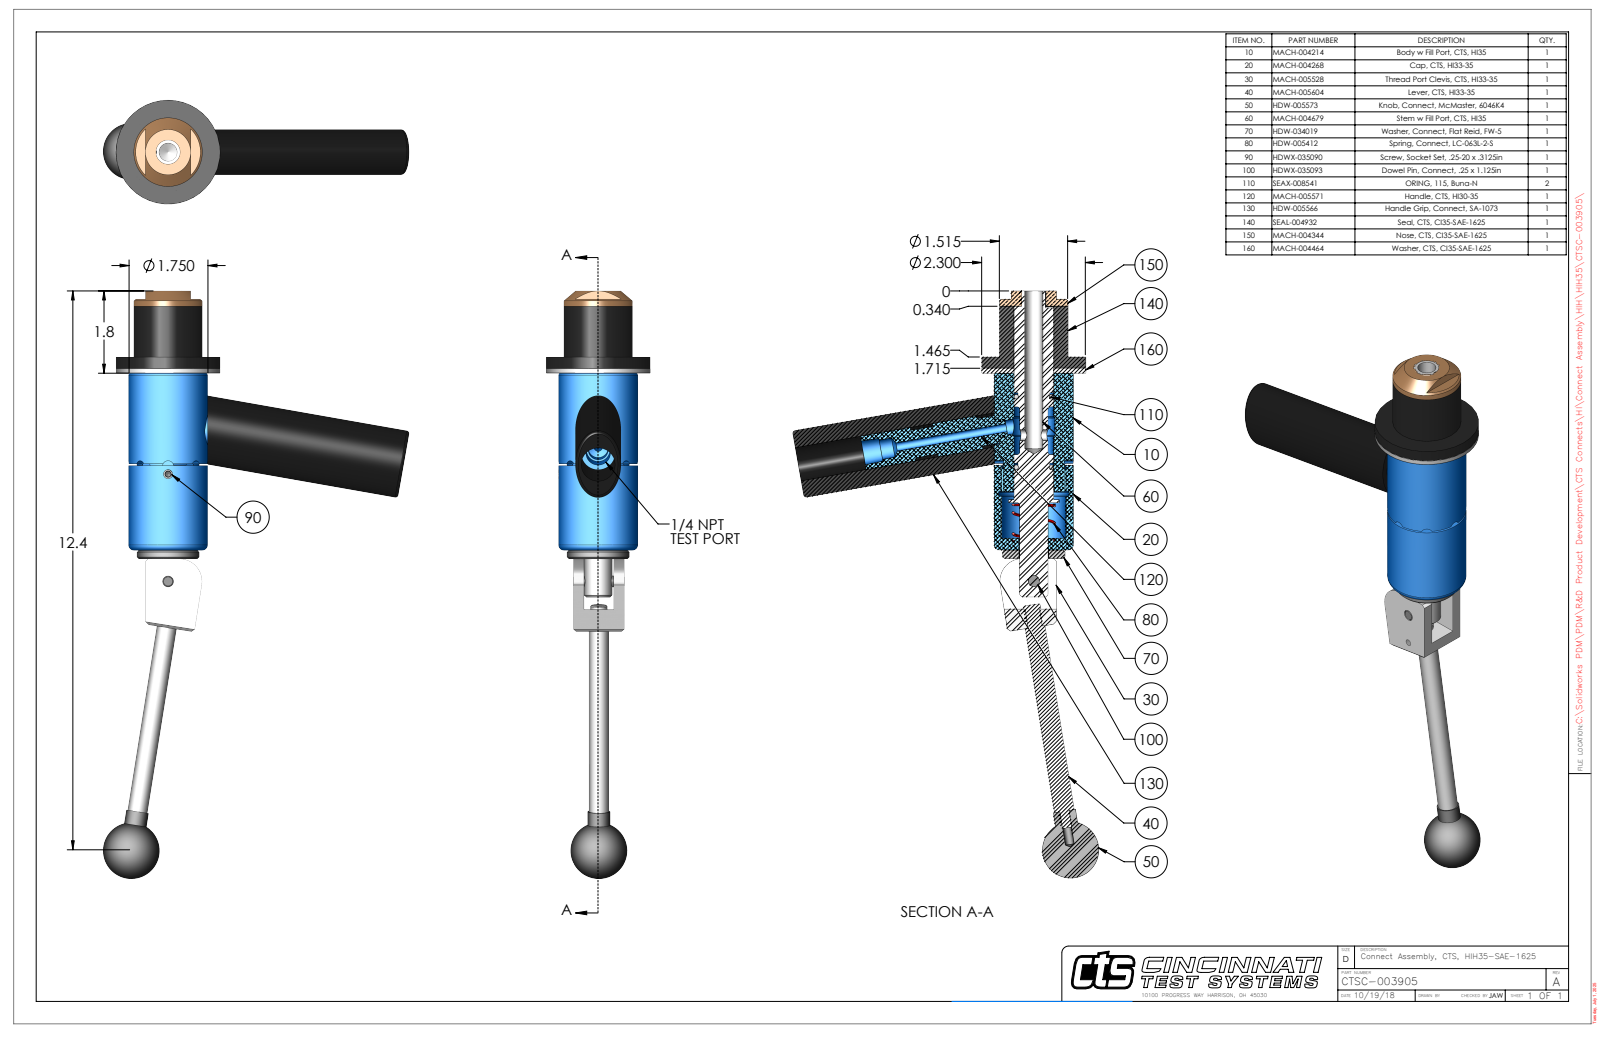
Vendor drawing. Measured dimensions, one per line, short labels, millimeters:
name: CTSC-003905
written by: SolidWorks 2023 (AUTOMOTIVE_DESIGN)
unit: mm
bodies: 11 solids, 294 faces (107 planar, 121 cylindrical, 66 other)
size: 330.7 × 171.8 × 58.4
volume: 336 600 mm³; area: 89 420 mm²
holes: 2× ⌀5.1, 1× ⌀3.8, 1× ⌀4.7, 1× ⌀6.3, 1× ⌀6.4, 1× ⌀6.4, 1× ⌀8, 1× ⌀10.3, 1× ⌀11.1, 1× ⌀13.5, 1× ⌀16.1, 1× ⌀16.7
bosses: 2× ⌀6.4, 1× ⌀58.4, 1× ⌀44.5, 1× ⌀38.5, 1× ⌀35.1, 1× ⌀22.1, 1× ⌀19.1, 1× ⌀15.9
rounds: 4× R3.2, 2× R0.7, 1× R6.3, 1× R8.4, 1× R12.7, 1× R17.7, 1× R20.8, 1× R21
face distances: 2.8, 34.9, 37.7, 137.3, 102.4, 99.6, 6.4, 28.6, 9.1, 108.7
hole spacings: 18.8, 60.4, 79.1
